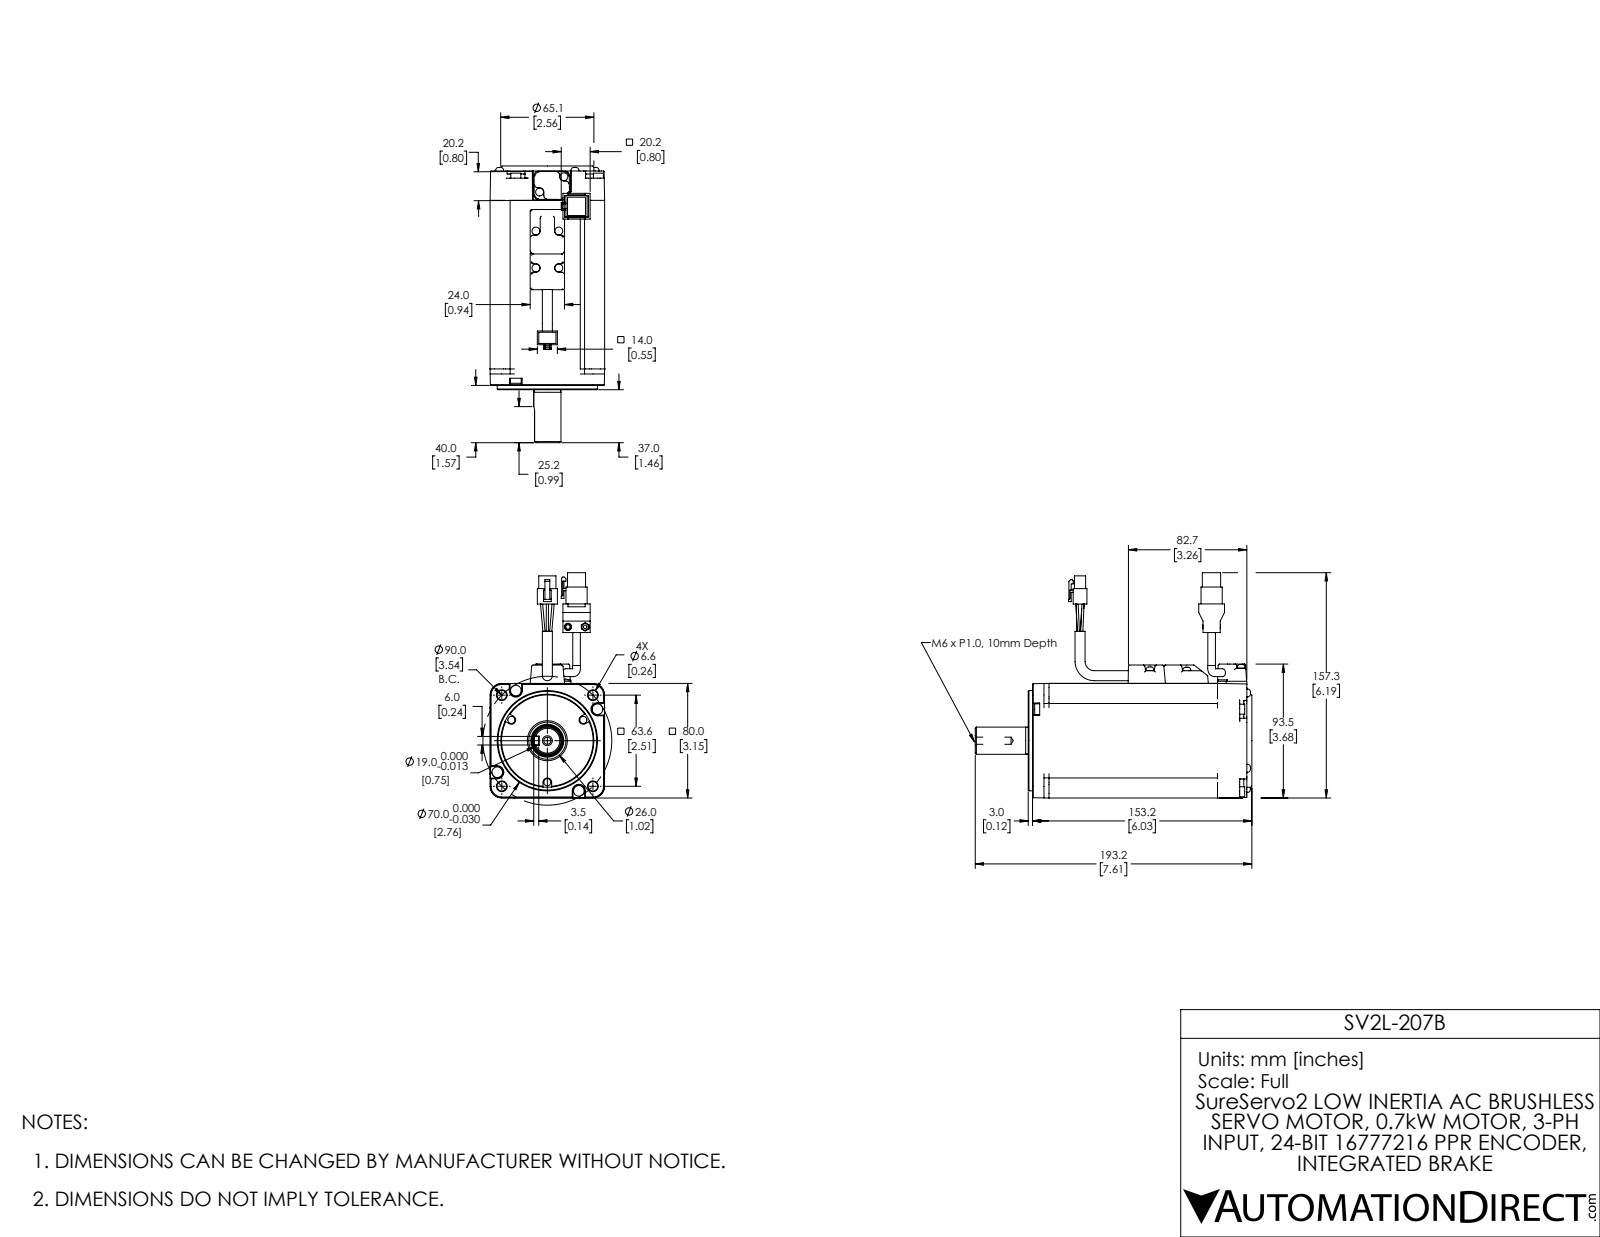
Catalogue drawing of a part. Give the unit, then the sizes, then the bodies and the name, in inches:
Units: inches
Overall size (bounding box): 7.606 × 6.193 × 3.15
Round holes (diameter × count): ⌀0.26 ×4, ⌀0.201 ×2, ⌀0.098 ×1, ⌀0.11 ×1, ⌀0.197 ×1, ⌀1.024 ×1, ⌀1.102 ×1, ⌀2.559 ×1
Round bosses / shafts (diameter × count): ⌀0.217 ×12, ⌀0.276 ×6, ⌀0.059 ×6, ⌀0.295 ×4, ⌀0.197 ×3, ⌀0.181 ×2, ⌀0.142 ×2, ⌀2.756 ×1
Partial cylindrical surfaces — rounded edges, fillets, slot ends (radius × count): R0.039 ×52, R0.118 ×28, R0.008 ×20, R0.079 ×20, R0.02 ×14, R0.012 ×12, R0.072 ×8, R0.073 ×8
Main face-to-face distances: 3.15, 0.551, 2.598, 3.151, 2.047, 6.13, 3.228, 0.138, 0.098, 6.031
Hole centre spacings: 1.772, 2.506, 3.543, 0.472, 1.889, 1.999, 2.614, 2.962
Volume: 55.6 in³ · Surface area: 115.8 in²
Bodies: 2 solids, 958 faces (367 planar, 327 cylindrical, 264 other)
Part name (STEP PRODUCT): ECM-A3H-CX0807SSX 207B r1C EXT red1
STEP written by: SolidWorks 2017 (AUTOMOTIVE_DESIGN)
